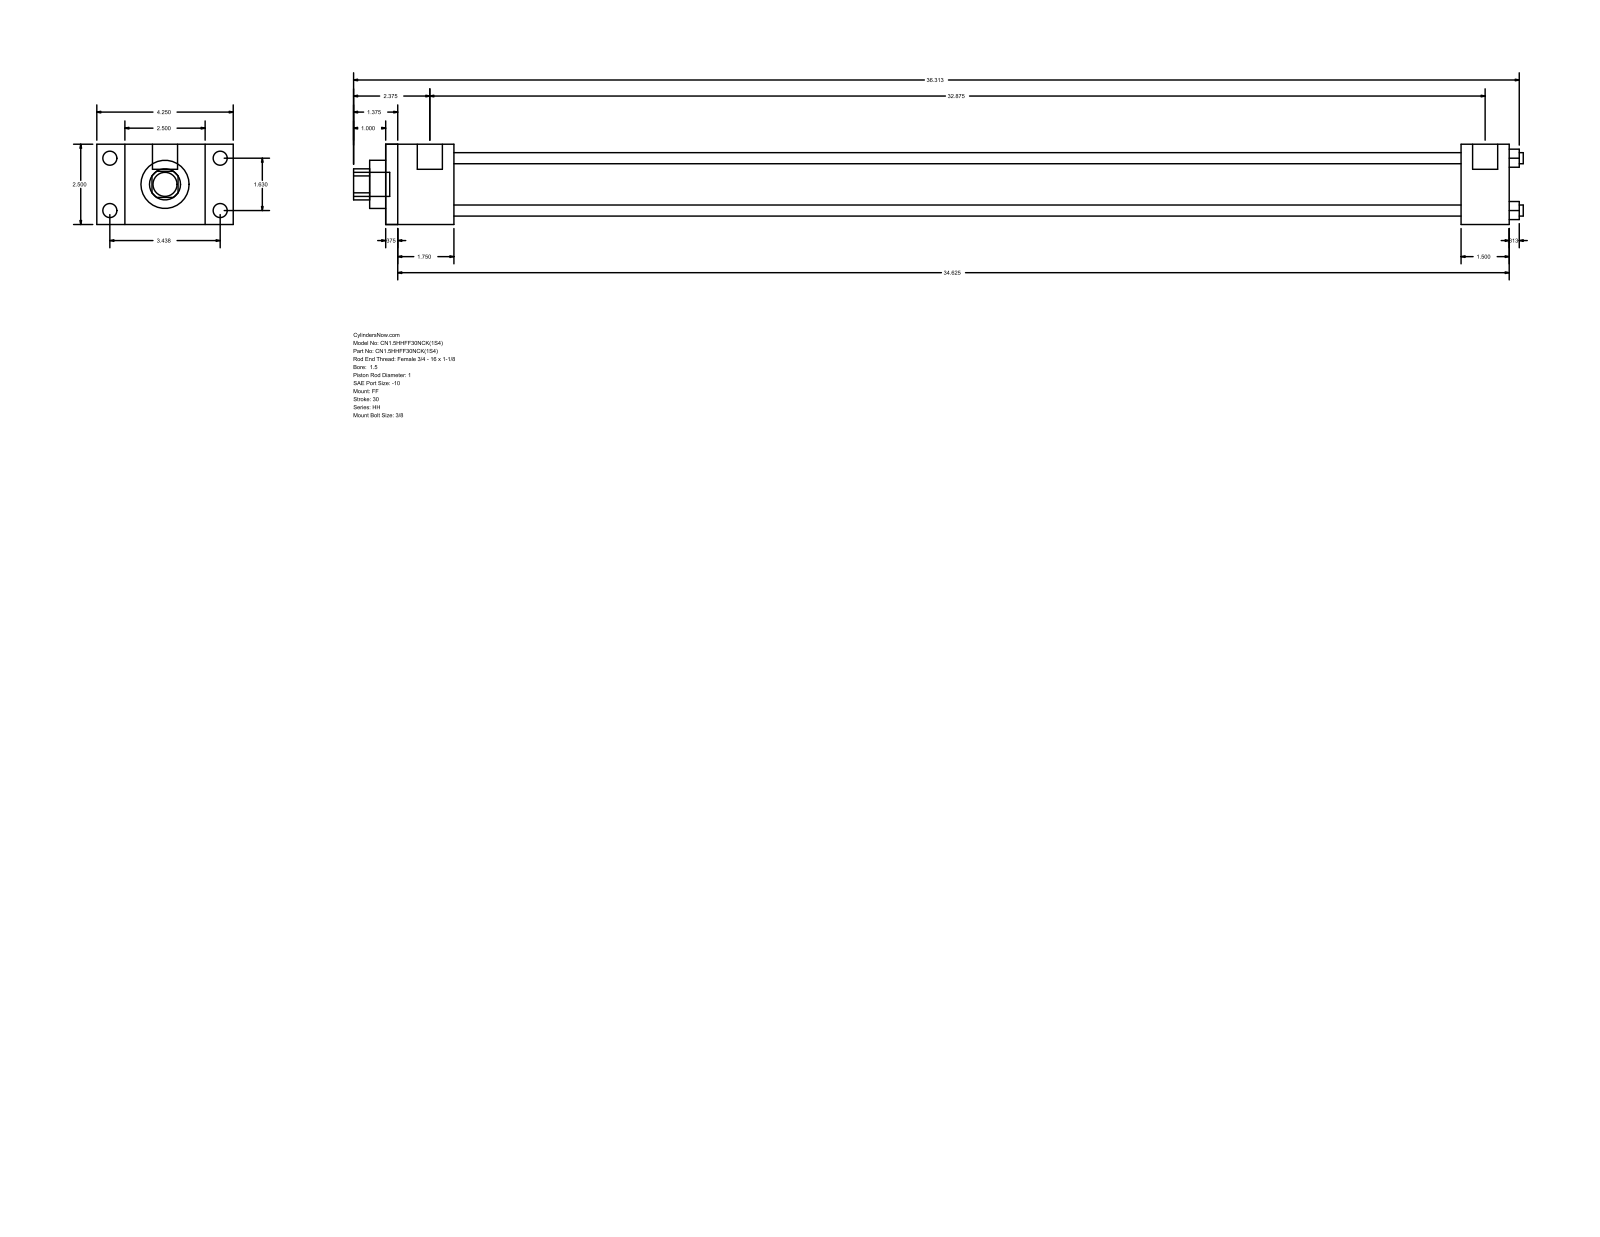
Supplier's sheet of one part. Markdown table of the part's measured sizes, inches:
| quantity | value |
| --- | --- |
| part name | HH_FF__0150_1 |
| STEP written by | GSSL Pune (CONFIG_CONTROL_DESIGN) |
| units | inches |
| bodies | 0 solids, 92 faces (64 planar, 28 cylindrical, 0 other) |
| overall size | 36.437 × 4.25 × 2.5 |
| round holes (diameter × count) | 0.345 × 4, 1 × 1, 1.5 × 1, 1.75 × 1 |
| round bosses / shafts (diameter × count) | 0.438 × 4, 0.219 × 4, 0.781 × 2, 0.75 × 1 |
| partial cylindrical surfaces (radius × count) | 0.484 × 1 |
| main face-to-face distances | 2.5, 35, 0.375, 34.625, 2.125, 1.75, 32.875, 33.5, 33.125, 31.375 |
| hole center spacings | 1.152, 1.63, 2.305 |
